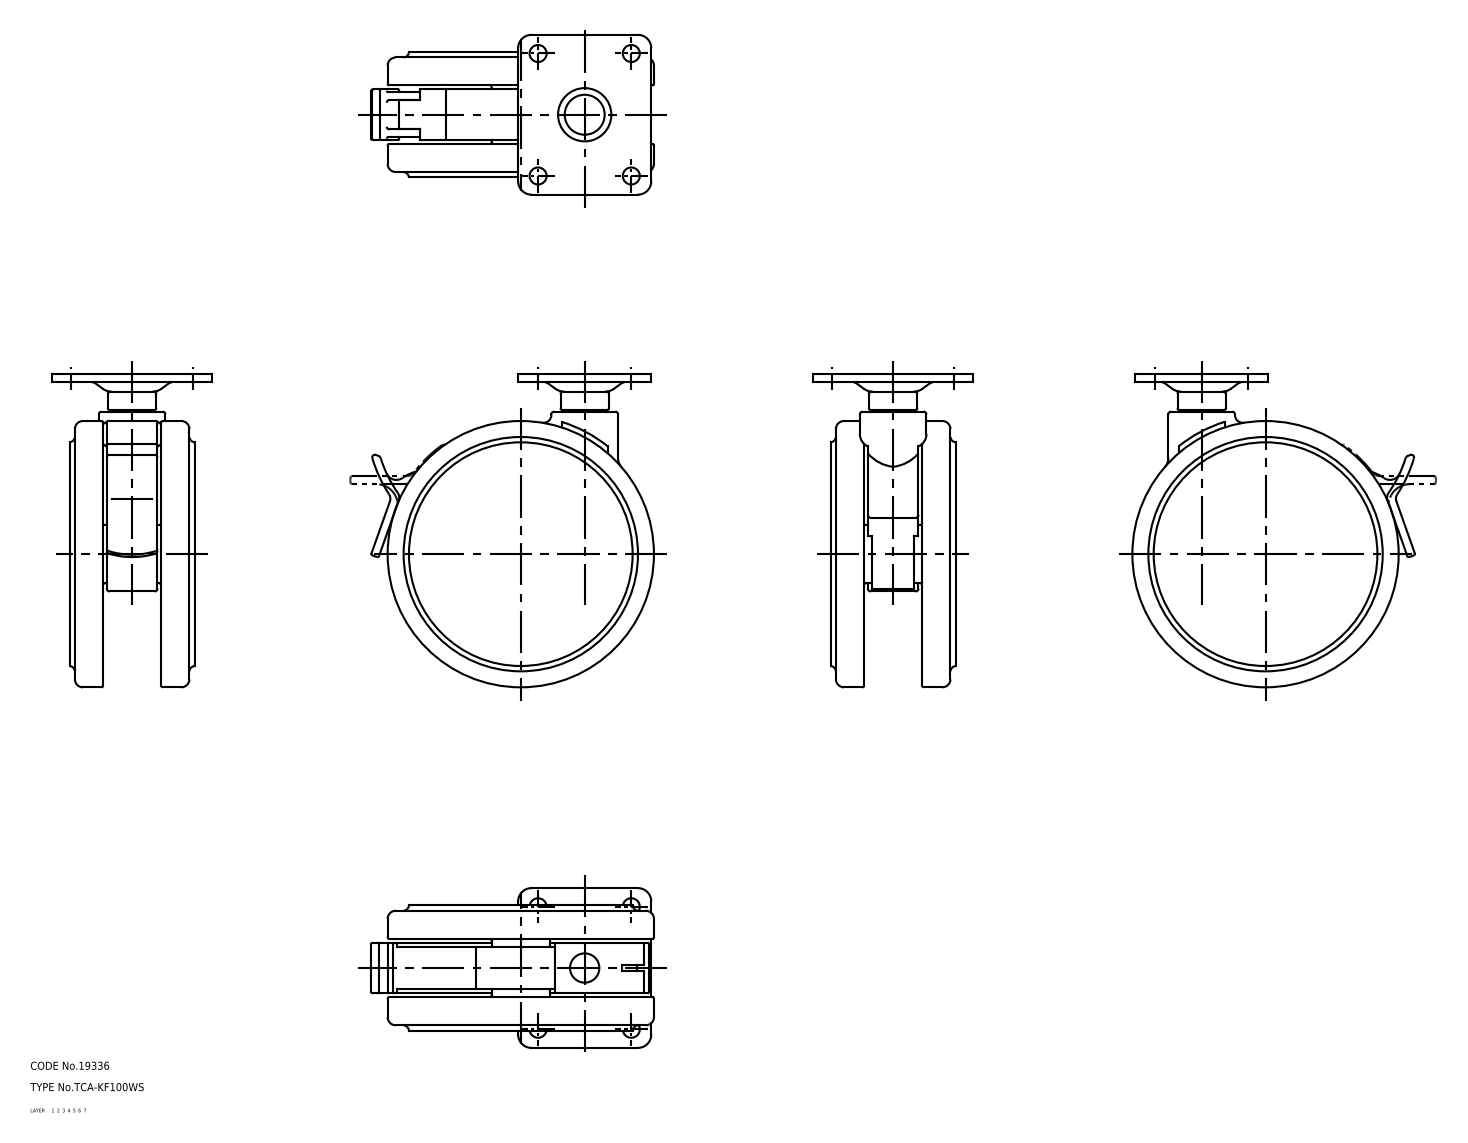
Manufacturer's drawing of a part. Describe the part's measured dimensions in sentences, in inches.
The part is named "mounting plate; lever; TCA_KF100WS; main shaft (+2 more)". Its 3-D file was written by "SolidWorks 2015 (AUTOMOTIVE_DESIGN)". It is 6 solids with 282 faces: 64 planar, 110 cylindrical and 108 other. Overall it measures 4.626 by 4.178 by 2.362 inches. Its volume is 14.68 cubic inches and its surface area 104.8 square inches. Round holes: 4 of diameter 0.252, 1 of diameter 0.236, 1 of diameter 2.835. Round bosses or shafts: 1 of diameter 3.937, 1 of diameter 0.984, 1 of diameter 0.866, 1 of diameter 0.709, 1 of diameter 0.669, 1 of diameter 0.591. Partial cylindrical surfaces (rounded edges, fillets, slot ends): 35 of radius 0.02, 4 of radius 0.197, 3 of radius 0.118, 2 of radius 0.039, 2 of radius 1.87, 1 of radius 0.059, 1 of radius 0.079, 1 of radius 0.157. The main face-to-face distances are 0.059, 0.492, 1.358, 0.295, 1.063, 1.555, 0.197, 0.118, 0.748, 0.551. The hole center spacings are 1.138, 1.378, 1.811, 2.276.
